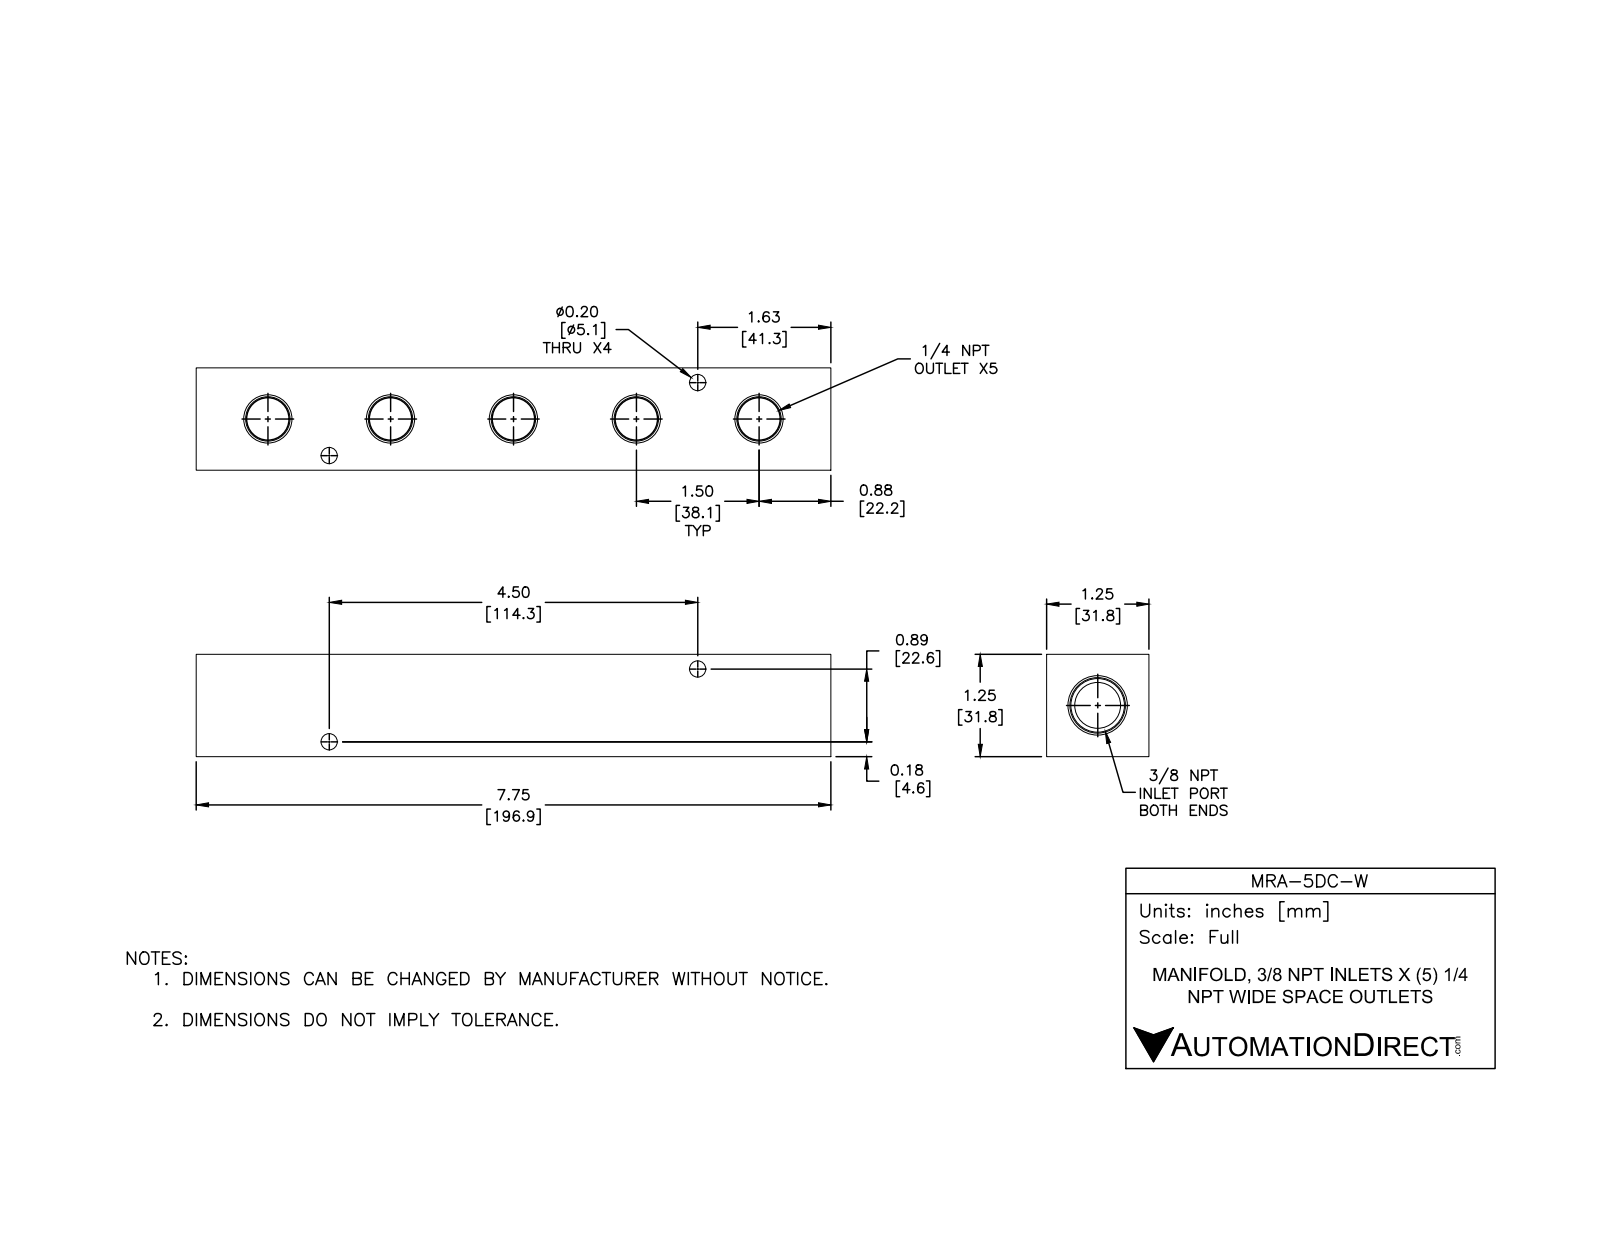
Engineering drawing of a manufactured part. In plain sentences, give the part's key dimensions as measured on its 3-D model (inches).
The part is named "MRA-5DC-W". Its 3-D file was written by "SolidWorks 2015 (CONFIG_CONTROL_DESIGN)". It is 1 solid with 74 faces: 18 planar, 28 cylindrical and 28 other. Overall it measures 7.75 by 1.25 by 1.25 inches. Its volume is 9.547 cubic inches and its surface area 58.99 square inches. Round holes: 4 of diameter 0.2, 1 of diameter 0.562. Partial cylindrical surfaces (rounded edges, fillets, slot ends): 5 of radius 0.219. The main face-to-face distances are 1.25, 7.75, 0.41, 7.34, 0.86, 0.39, 6.93. The hole center spacings are 4.587.
